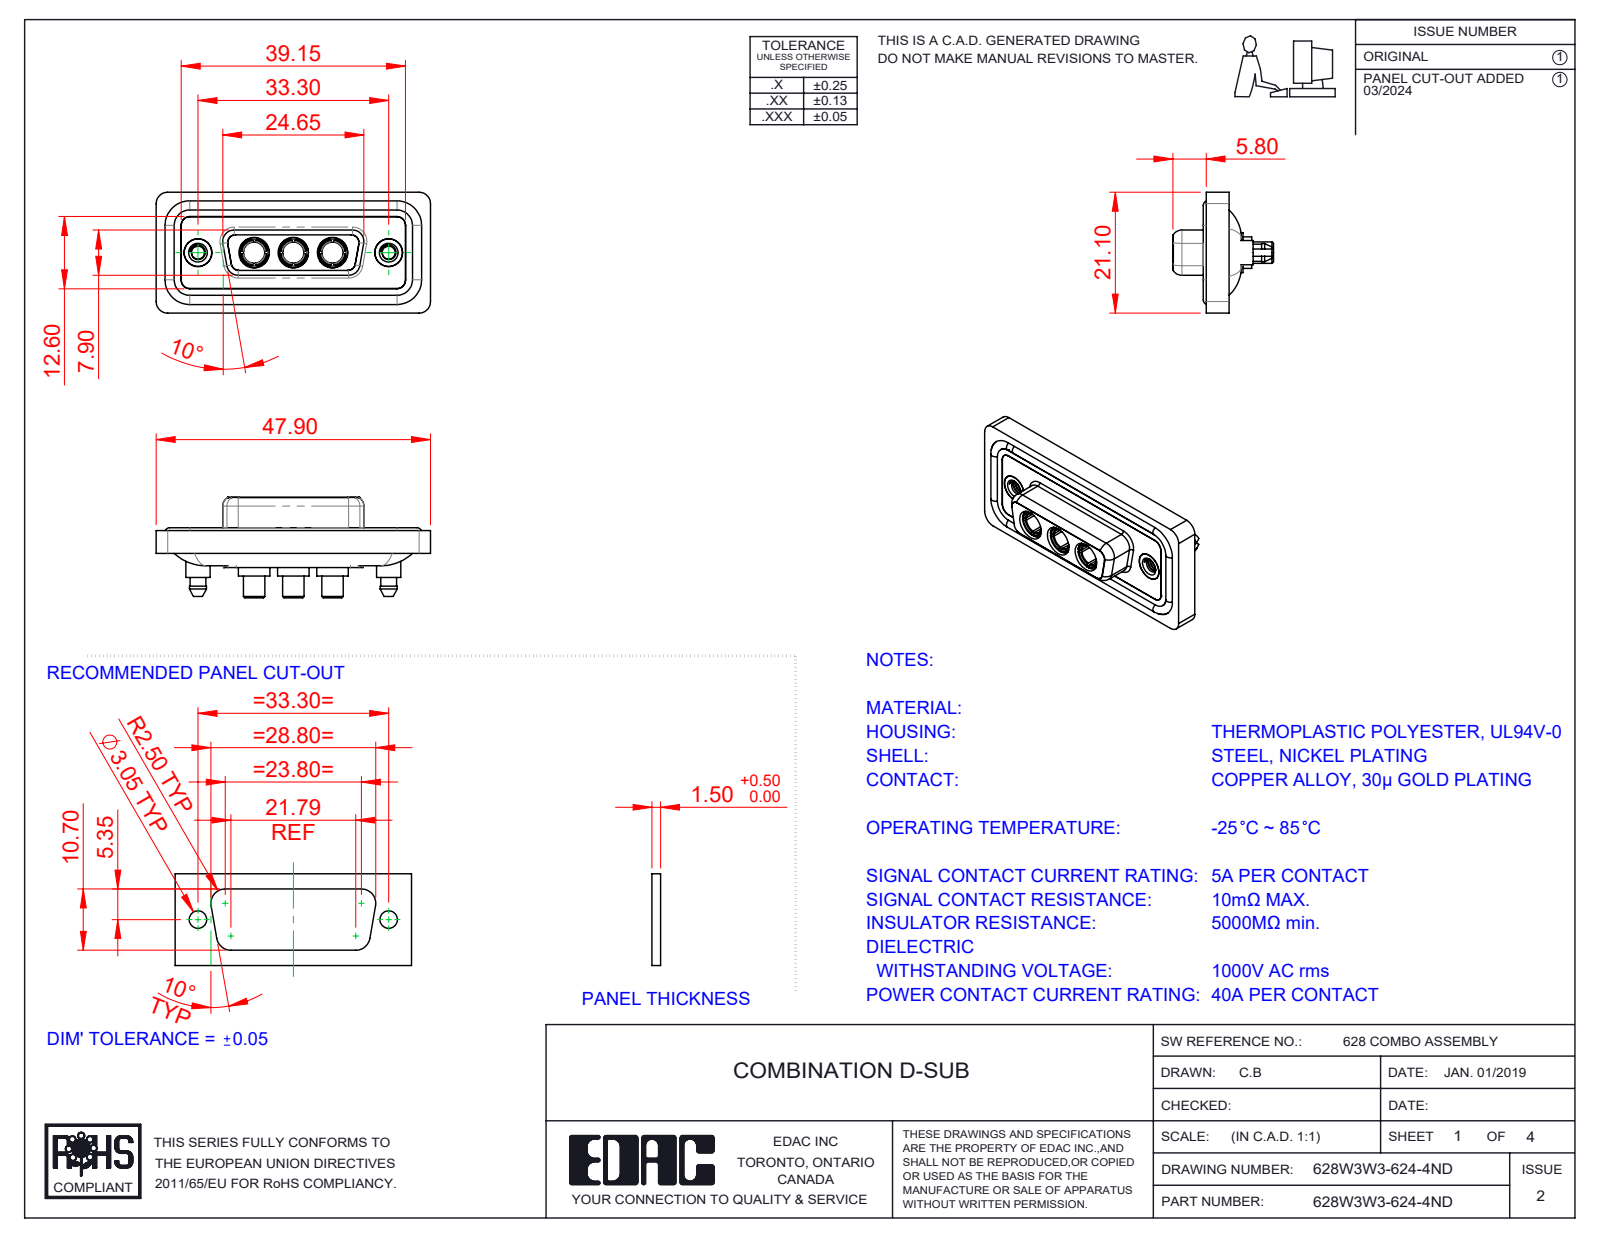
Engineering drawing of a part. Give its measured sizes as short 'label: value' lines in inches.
name: 628Combo Housing_3W3; Power Socket_40A S; 628Combo Waterproof Housing_15 Contacts; 628Combo Shell Rear_15 Contacts (+3 more)
written by: SolidWorks 2023 (CONFIG_CONTROL_DESIGN)
unit: in
bodies: 13 solids, 674 faces (208 planar, 305 cylindrical, 161 other)
size: 1.886 × 0.831 × 0.691
volume: 0.379 in³; area: 15.67 in²
holes: 5× ⌀0.191, 3× ⌀0.146, 3× ⌀0.209, 2× ⌀0.089, 2× ⌀0.157, 2× ⌀0.159, 2× ⌀0.197
bosses: 4× ⌀0.063, 3× ⌀0.217, 3× ⌀0.205, 3× ⌀0.195, 3× ⌀0.187, 3× ⌀0.148, 2× ⌀0.213, 2× ⌀0.195
rounds: 24× R0.059, 20× R0.079, 12× R0.053, 10× R0.063, 4× R0.01, 4× R0.02, 4× R0.024, 4× R0.026
face distances: 0.016, 0.071, 0.063, 0.02, 0.293, 0.043, 0.114, 0.222, 0.278, 0.26
hole spacings: 0.27, 0.386, 0.656, 0.925, 0.539, 1.311
